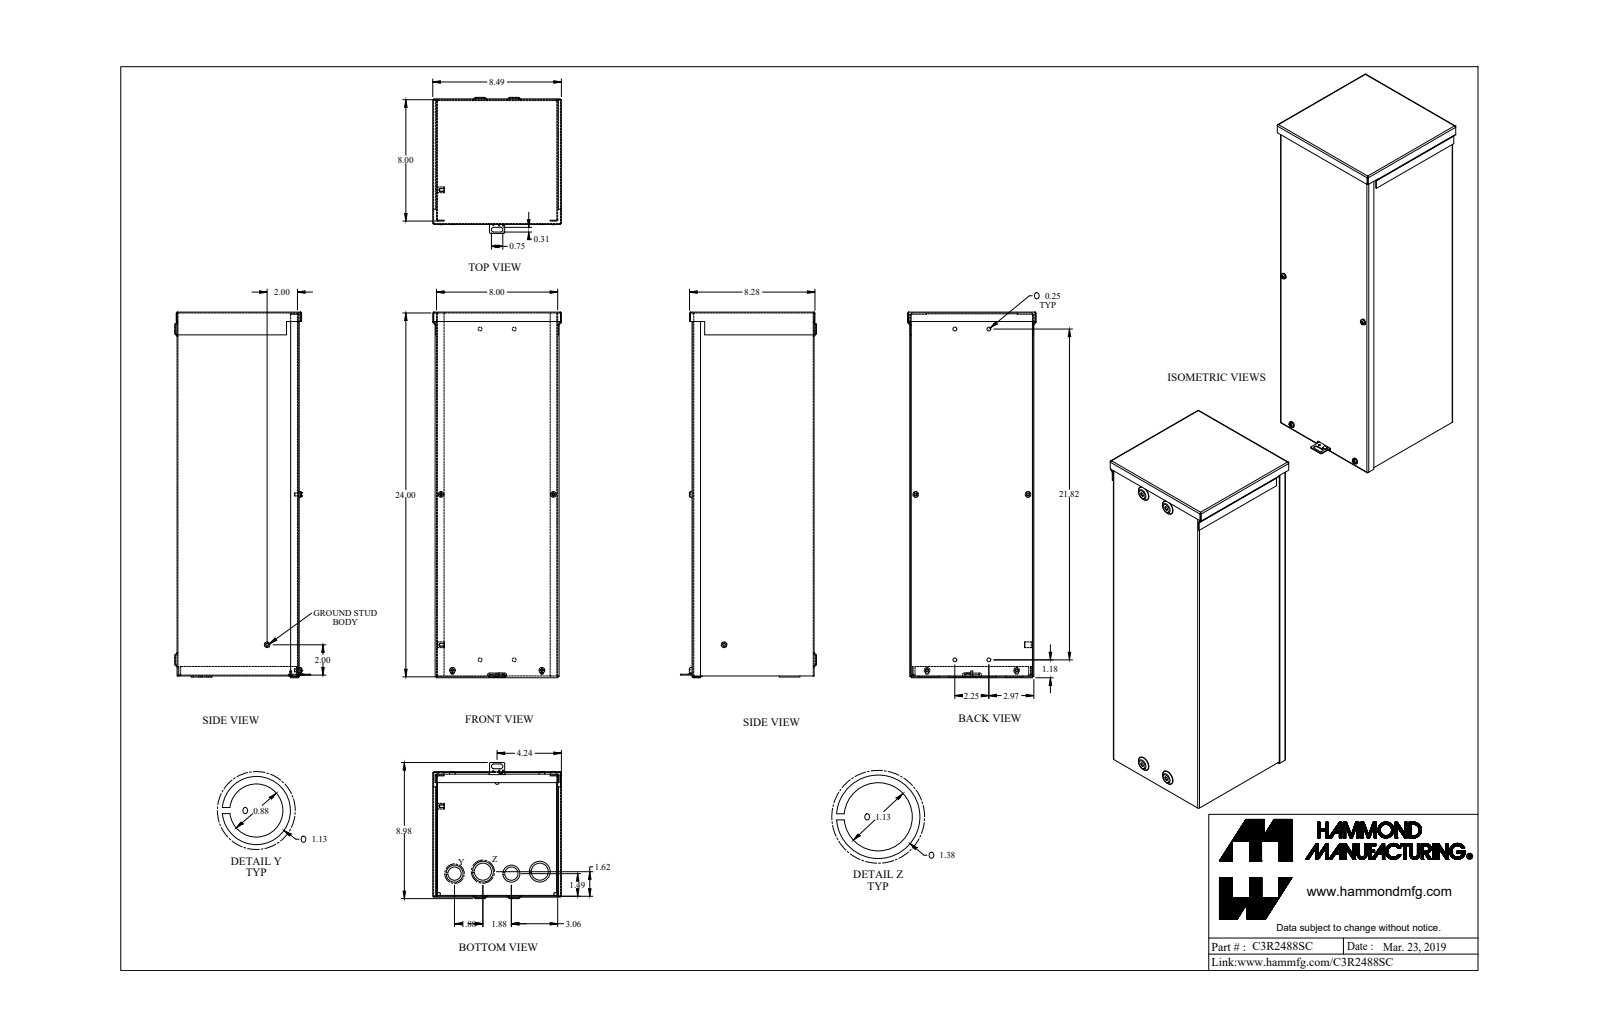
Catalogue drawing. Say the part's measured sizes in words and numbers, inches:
The part is named "C3R2488SC_Default". Its 3-D file was written by "SolidWorks 2019 (CONFIG_CONTROL_DESIGN)". It is 11 solids with 424 faces: 223 planar, 115 cylindrical and 86 other. Overall it measures 24.12 by 8.977 by 8.489 inches. Its volume is 57.1 cubic inches and its surface area 2 015 square inches. Round holes: 4 of diameter 0.17, 4 of diameter 0.25, 2 of diameter 1.125, 1 of diameter 0.125, 1 of diameter 0.137, 1 of diameter 0.156, 1 of diameter 0.875, 1 of diameter 0.875. Round bosses or shafts: 4 of diameter 0.375, 4 of diameter 0.19, 2 of diameter 1.375, 2 of diameter 1.125, 1 of diameter 0.375, 1 of diameter 0.125. Partial cylindrical surfaces (rounded edges, fillets, slot ends): 21 of radius 0.029, 21 of radius 0.086, 8 of radius 0.109, 8 of radius 0.125, 2 of radius 0.156. The main face-to-face distances are 0.057, 7.943, 8, 7.886, 8.057, 0.057, 23.886, 23.943, 23.943, 24. The hole center spacings are 11.211, 11.931, 1.88, 1.998, 2.25, 3.75, 4.165, 11.702.
